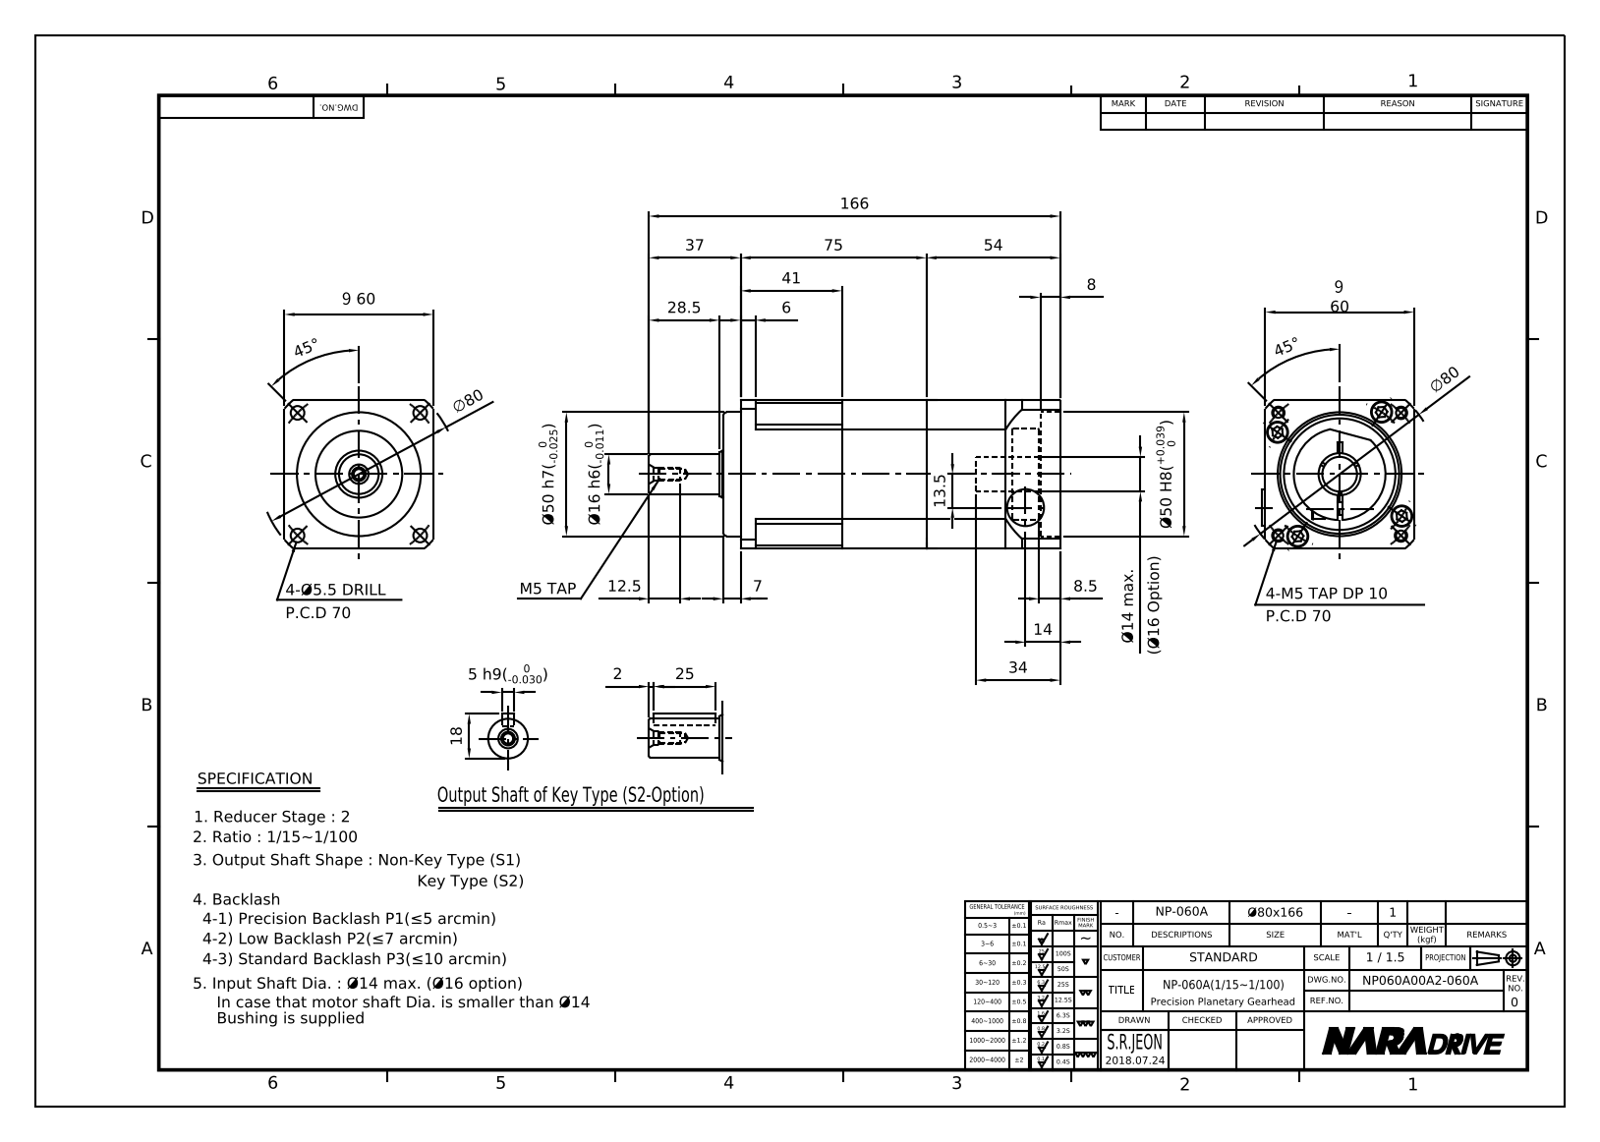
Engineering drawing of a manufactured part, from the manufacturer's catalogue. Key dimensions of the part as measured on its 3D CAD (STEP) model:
Part name (STEP PRODUCT): NP060A00A2-060A-S1
STEP written by: Autodesk Inventor 2015 (AUTOMOTIVE_DESIGN)
Units: millimetres
Bodies: 2 solids, 318 faces (147 planar, 90 cylindrical, 81 other)
Overall size (bounding box): 166 × 61.5 × 60
Volume: 276 214 mm³ · Surface area: 70 377 mm²
Round holes (diameter × count): ⌀4.13 ×9, ⌀5.5 ×9, ⌀3.24 ×4, ⌀4.2 ×4, ⌀7.5 ×4, ⌀9 ×4, ⌀7 ×1, ⌀8.5 ×1, ⌀14 ×1, ⌀17 ×1, ⌀45 ×1, ⌀48 ×1
Round bosses / shafts (diameter × count): ⌀8.5 ×5, ⌀5 ×5, ⌀37 ×1, ⌀35 ×1, ⌀19 ×1, ⌀16 ×1, ⌀15 ×1, ⌀8 ×1
Partial cylindrical surfaces — rounded edges, fillets, slot ends (radius × count): R0.5 ×4, R7 ×4, R2.07 ×1, R4.5 ×1, R35 ×1, R40 ×1
Main face-to-face distances: 60, 39, 7, 46, 129, 136, 90, 19.5, 116.5, 109.5
Hole centre spacings: 30.25, 42.78, 50.74, 51.15, 64.83, 7.84, 8.77, 12.58
